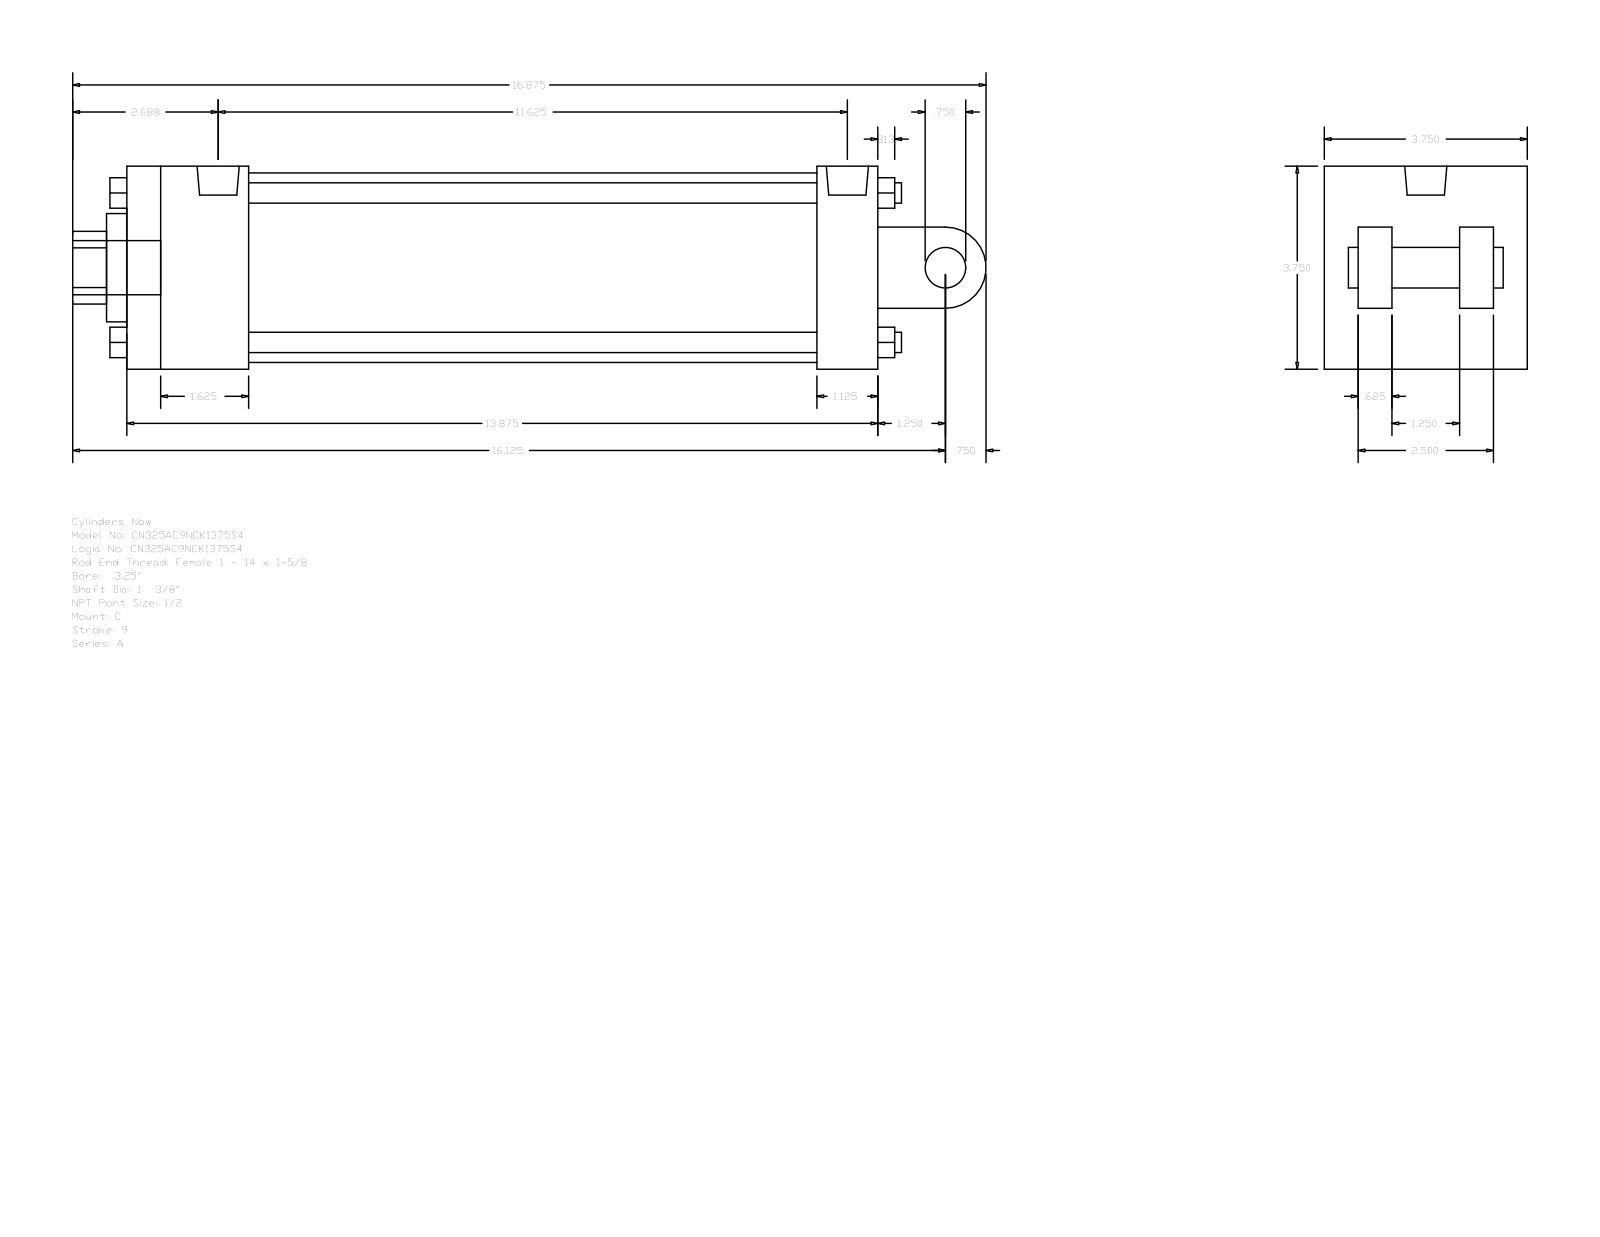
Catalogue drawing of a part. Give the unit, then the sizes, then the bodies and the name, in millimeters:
Units: millimetres
Overall size (bounding box): 428.62 × 95.25 × 95.25
Round holes (diameter × count): ⌀8.73 ×2, ⌀19.77 ×1, ⌀34.92 ×1, ⌀50.8 ×1, ⌀88.9 ×1
Round bosses / shafts (diameter × count): ⌀9.53 ×4, ⌀8.73 ×2, ⌀25.4 ×1, ⌀19.77 ×1, ⌀19.05 ×1
Partial cylindrical surfaces — rounded edges, fillets, slot ends (radius × count): R17.06 ×1, R19.05 ×1
Main face-to-face distances: 95.24, 15.87, 352.42, 28.57, 63.5, 66.67, 79.37, 31.74, 47.63, 323.85
Hole centre spacings: 3.18
Bodies: 0 solids, 135 faces (102 planar, 33 cylindrical, 0 other)
Part name (STEP PRODUCT): A_C__0325_1.375
STEP written by: GSSL Pune (CONFIG_CONTROL_DESIGN)
